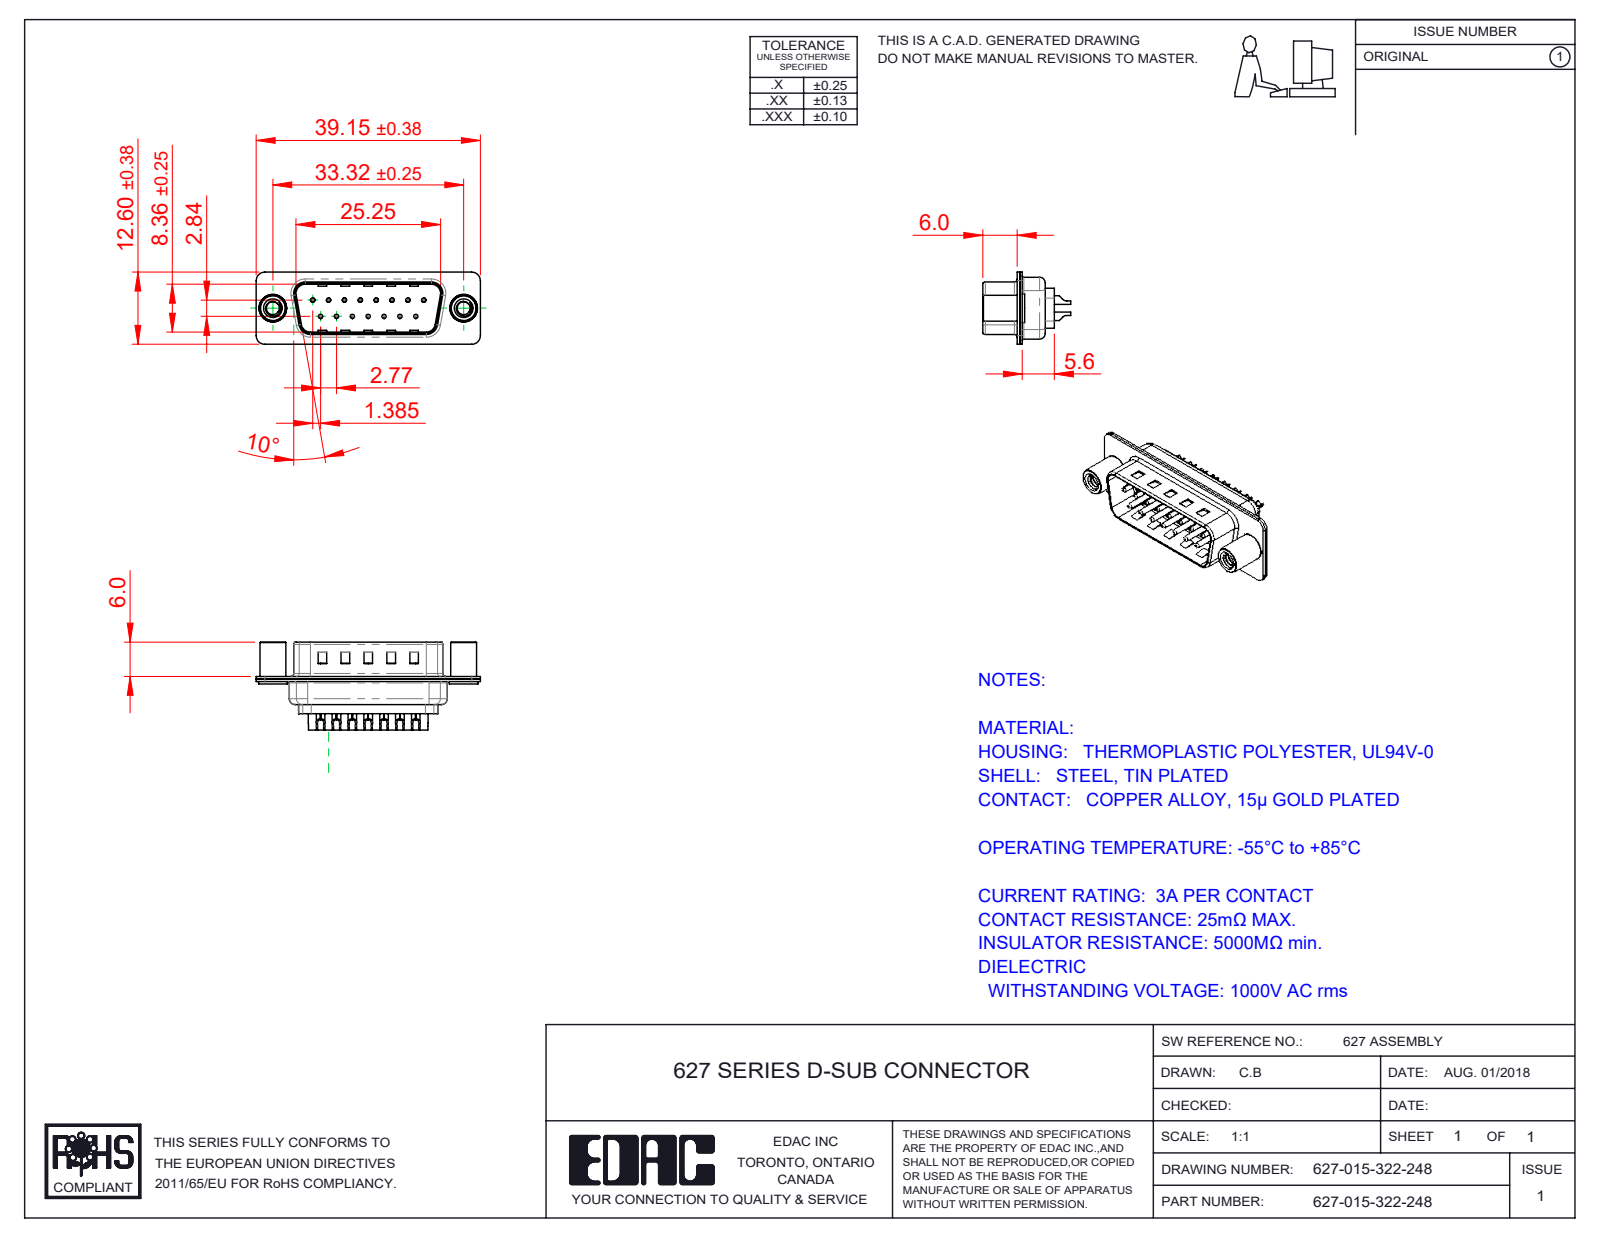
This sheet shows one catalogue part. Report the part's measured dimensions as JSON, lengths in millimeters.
{"part_name": "627 Shell Rear_15 Contacts; 627 Contact Row 1_22L; 627 4-40 Threaded Standoff; 627 Housing_15 LP (+3 more)", "step_written_by": "SolidWorks 2020 (CONFIG_CONTROL_DESIGN)", "units": "millimeters", "bodies": {"solids": 20, "faces": 1334, "planar": 351, "cylindrical": 596, "other": 387}, "overall_size": [39.15, 15.35, 12.6], "volume_mm3": 1899, "surface_area_mm2": 5618, "round_holes": [[0.35, 15], [1.1, 15], [1.6, 15], [2.26, 2], [4, 2], [4.8, 2]], "round_bosses_or_shafts": [[2, 15], [1.5, 15], [0.75, 15], [5, 2], [4.9, 2], [4.5, 2]], "partial_cylinders_radius": [[1.5, 16], [2, 12], [0.5, 8], [1.6, 8], [1, 6], [0.25, 4], [0.6, 4], [0.65, 4]], "face_to_face_distances": [0.4, 0.45, 0.9, 0.82, 9.58, 8.76, 1.5, 1.4, 6.5, 5.6], "hole_center_spacings": [3.16, 2.77, 5.54, 8.31, 11.08, 5.03, 5.04, 7.48]}
